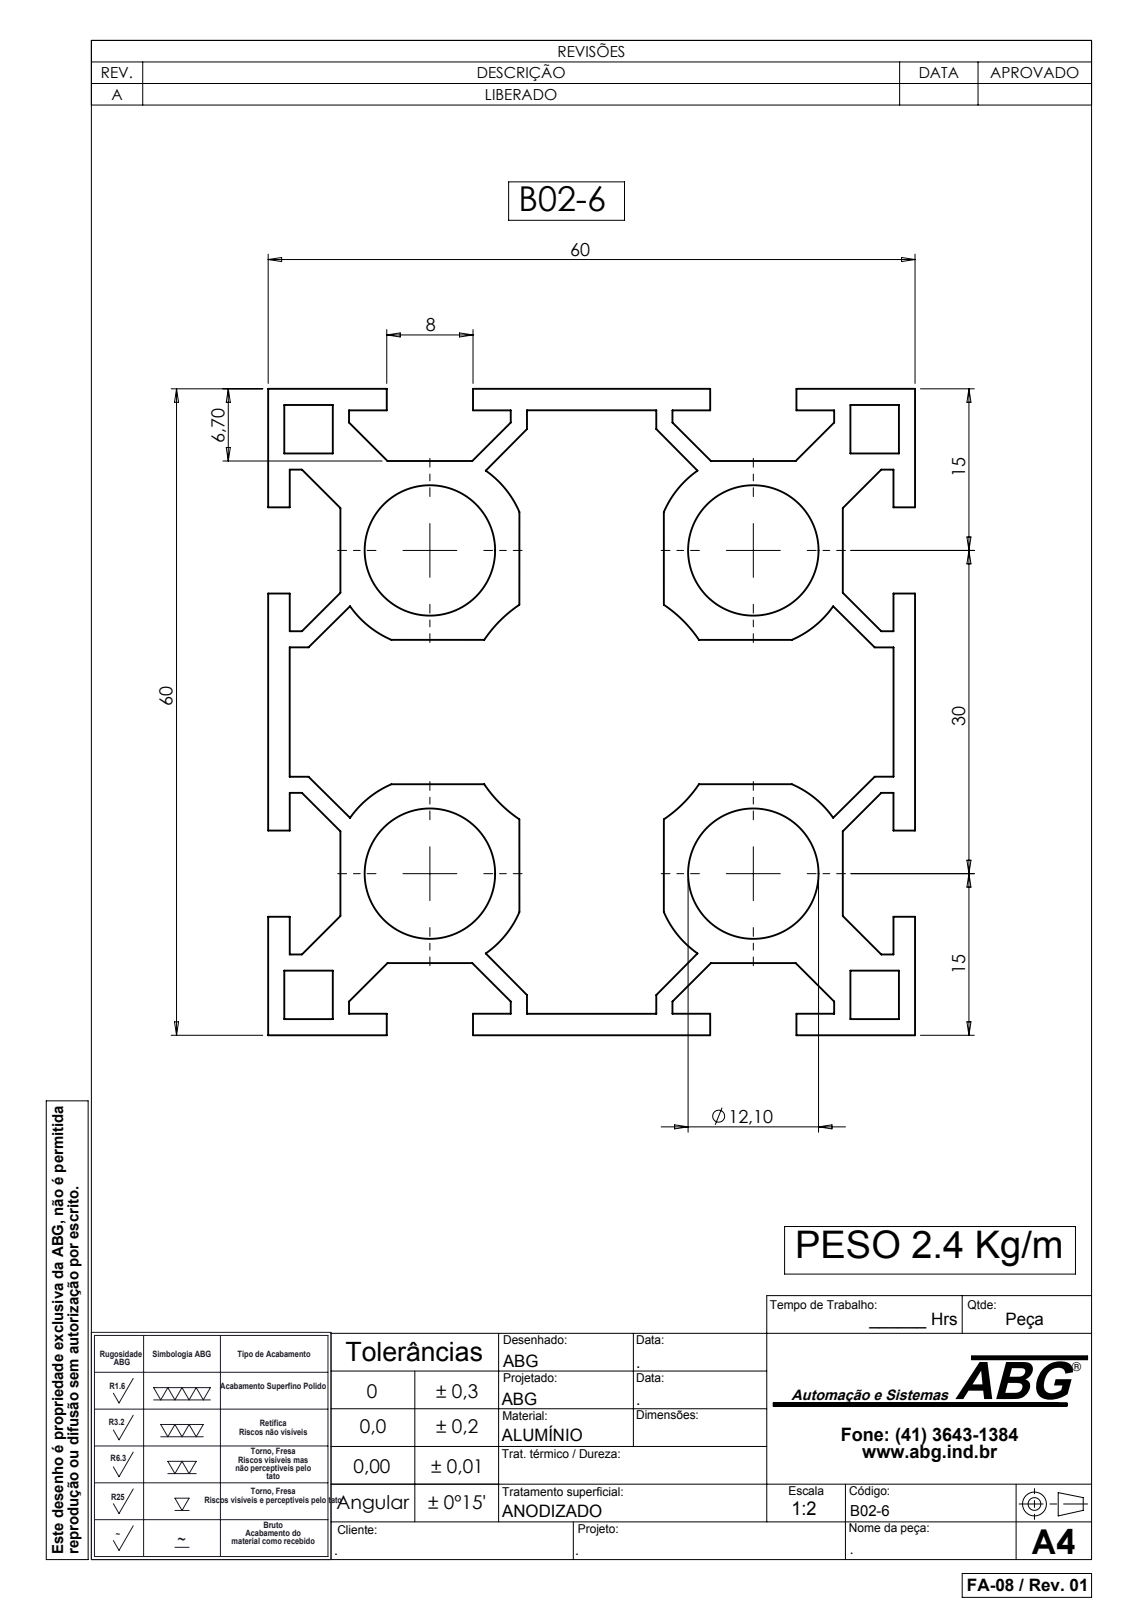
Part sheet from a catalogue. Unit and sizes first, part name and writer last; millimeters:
Units: millimetres
Overall size (bounding box): 6000 × 60 × 60
Round holes (diameter × count): ⌀12.1 ×4
Partial cylindrical surfaces — rounded edges, fillets, slot ends (radius × count): R9.04 ×4, R12 ×1
Main face-to-face distances: 60, 58, 2, 30, 53.3, 6.7, 51.3, 4.7, 36.7, 23.3
Hole centre spacings: 30, 42.43
Volume: 6 343 000 mm³ · Surface area: 5 298 000 mm²
Bodies: 1 solid, 150 faces (130 planar, 20 cylindrical, 0 other)
Part name (STEP PRODUCT): B02-6
STEP written by: SolidWorks 2007 (CONFIG_CONTROL_DESIGN)
